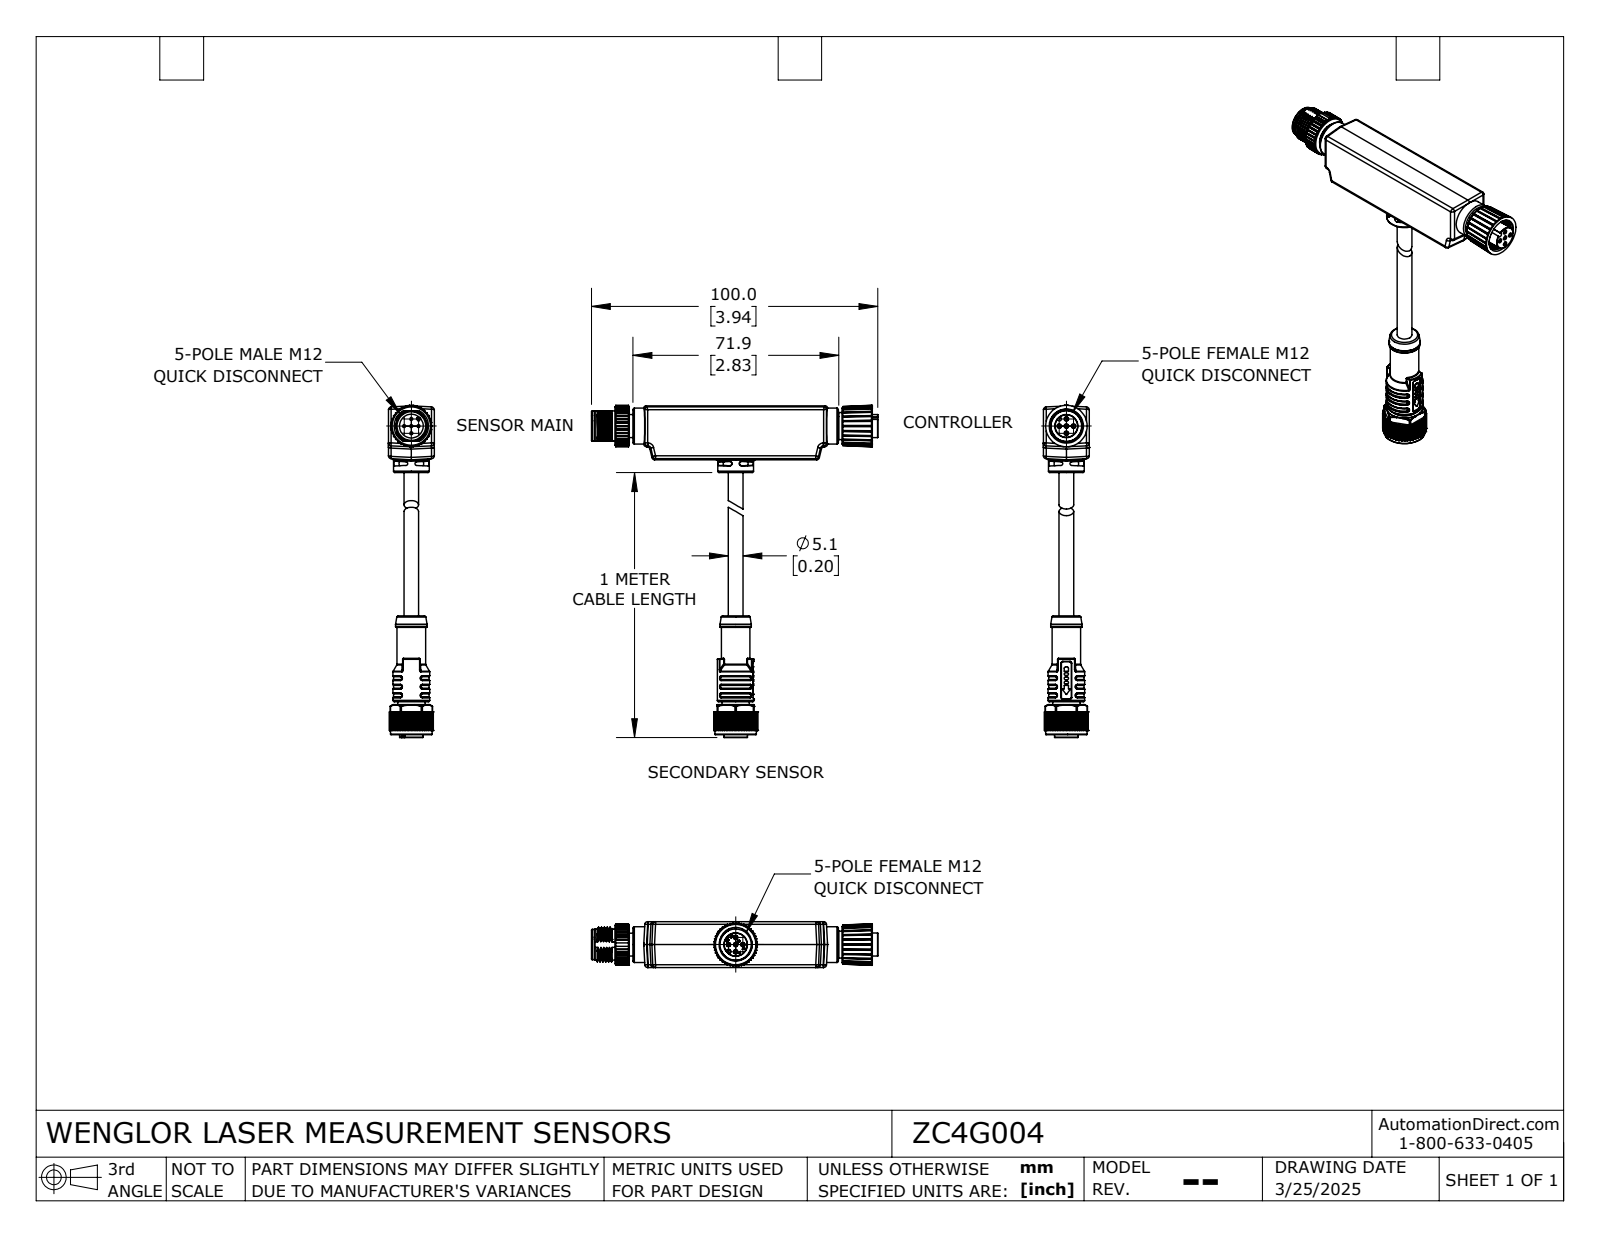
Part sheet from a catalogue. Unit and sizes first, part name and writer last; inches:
Units: inches
Overall size (bounding box): 4.567 × 3.937 × 0.63
Round holes (diameter × count): ⌀0.047 ×10, ⌀0.43 ×2, ⌀0.327 ×1, ⌀0.378 ×1, ⌀0.437 ×1
Round bosses / shafts (diameter × count): ⌀0.039 ×5, ⌀0.571 ×2, ⌀0.492 ×2, ⌀0.421 ×2, ⌀0.504 ×1, ⌀0.433 ×1, ⌀0.424 ×1, ⌀0.417 ×1
Partial cylindrical surfaces — rounded edges, fillets, slot ends (radius × count): R0.004 ×110, R0.028 ×64, R0.02 ×29, R0.039 ×26, R0.012 ×19, R0.008 ×12, R0.006 ×6, R0.031 ×4
Main face-to-face distances: 0.63, 0.739, 0.428, 0.039, 0.051, 3.291, 0.453, 0.492, 0.197, 0.35
Hole centre spacings: 0.139, 0.098, 0.197, 0.099, 0.197
Volume: 1.695 in³ · Surface area: 18.51 in²
Bodies: 2 solids, 1417 faces (560 planar, 519 cylindrical, 338 other)
Part name (STEP PRODUCT): ZC4G004
STEP written by: SolidWorks 2024 (AUTOMOTIVE_DESIGN)
